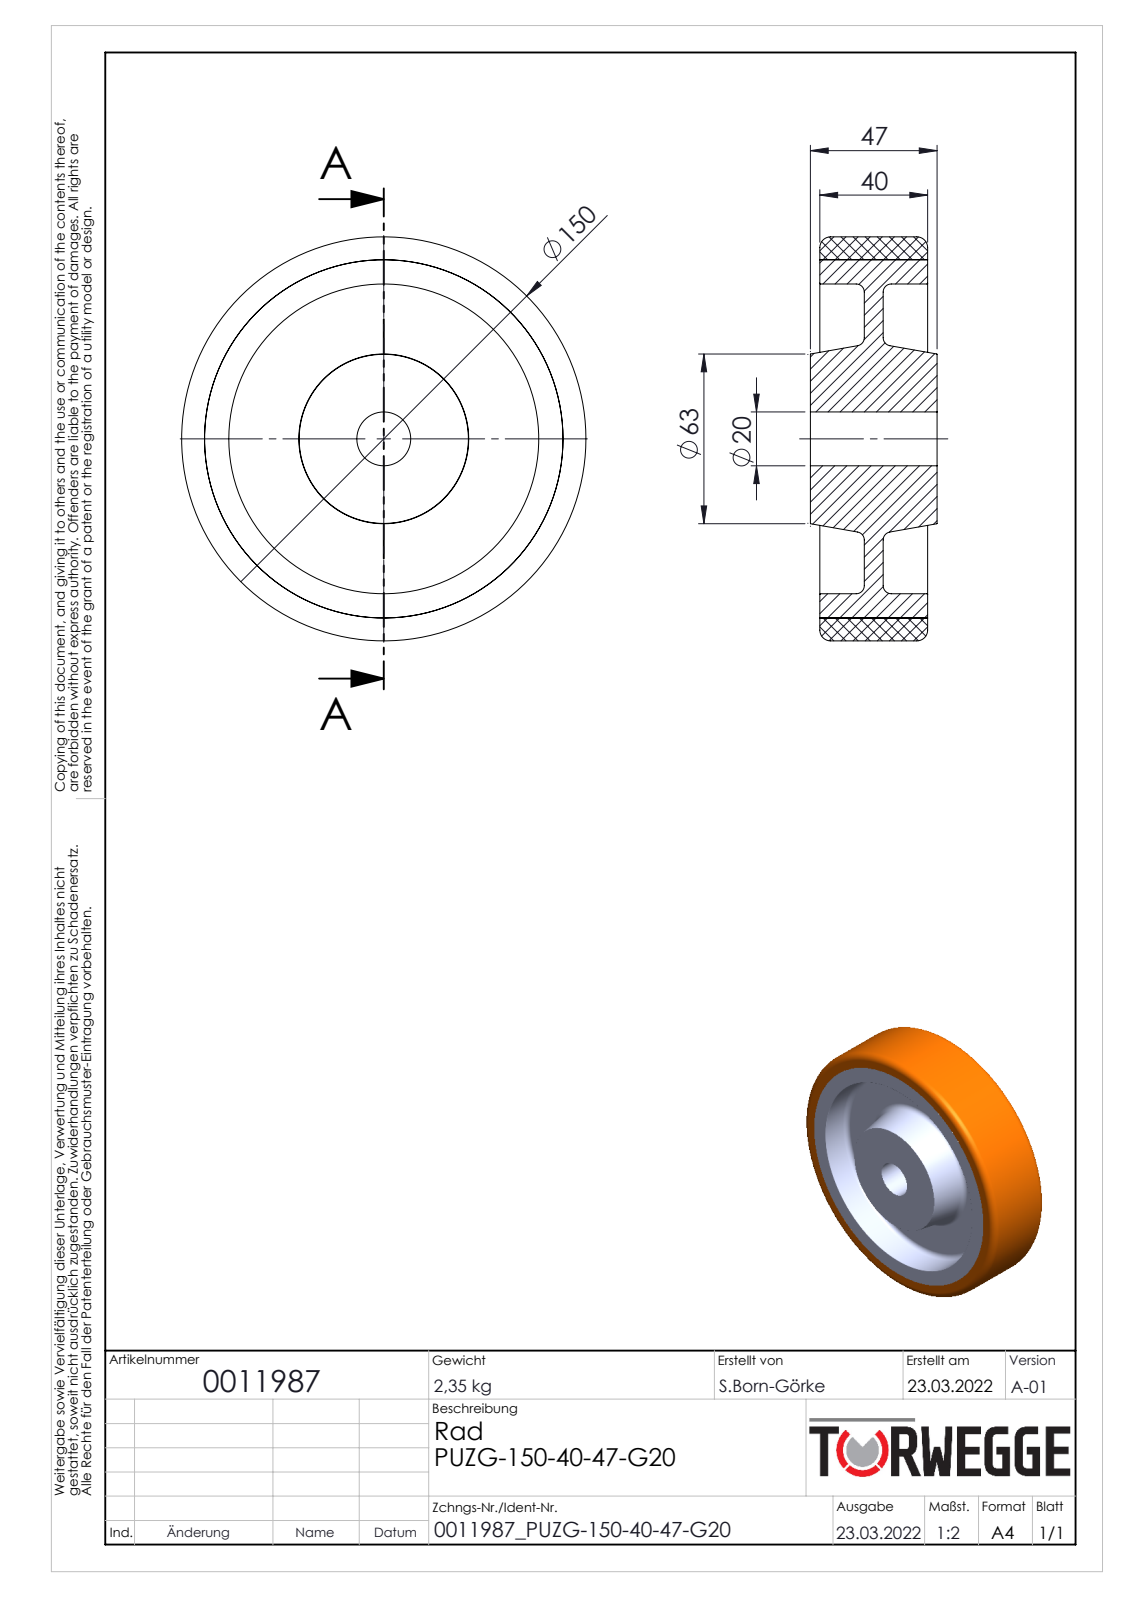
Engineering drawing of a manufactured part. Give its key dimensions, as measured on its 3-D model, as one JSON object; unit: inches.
{"part_name": "0011987", "step_written_by": "SolidWorks 2020 (AUTOMOTIVE_DESIGN)", "units": "inches", "bodies": {"solids": 2, "faces": 44, "planar": 8, "cylindrical": 12, "other": 24}, "overall_size": [5.906, 5.906, 1.85], "volume_in3": 29.73, "surface_area_in2": 164, "round_holes": [[0.787, 1], [4.528, 1], [5.236, 1]], "round_bosses_or_shafts": [[5.906, 1]], "face_to_face_distances": [0.65, 0.925, 0.138, 0.787, 1.063, 1.713, 1.575, 0.276, 1.85]}
